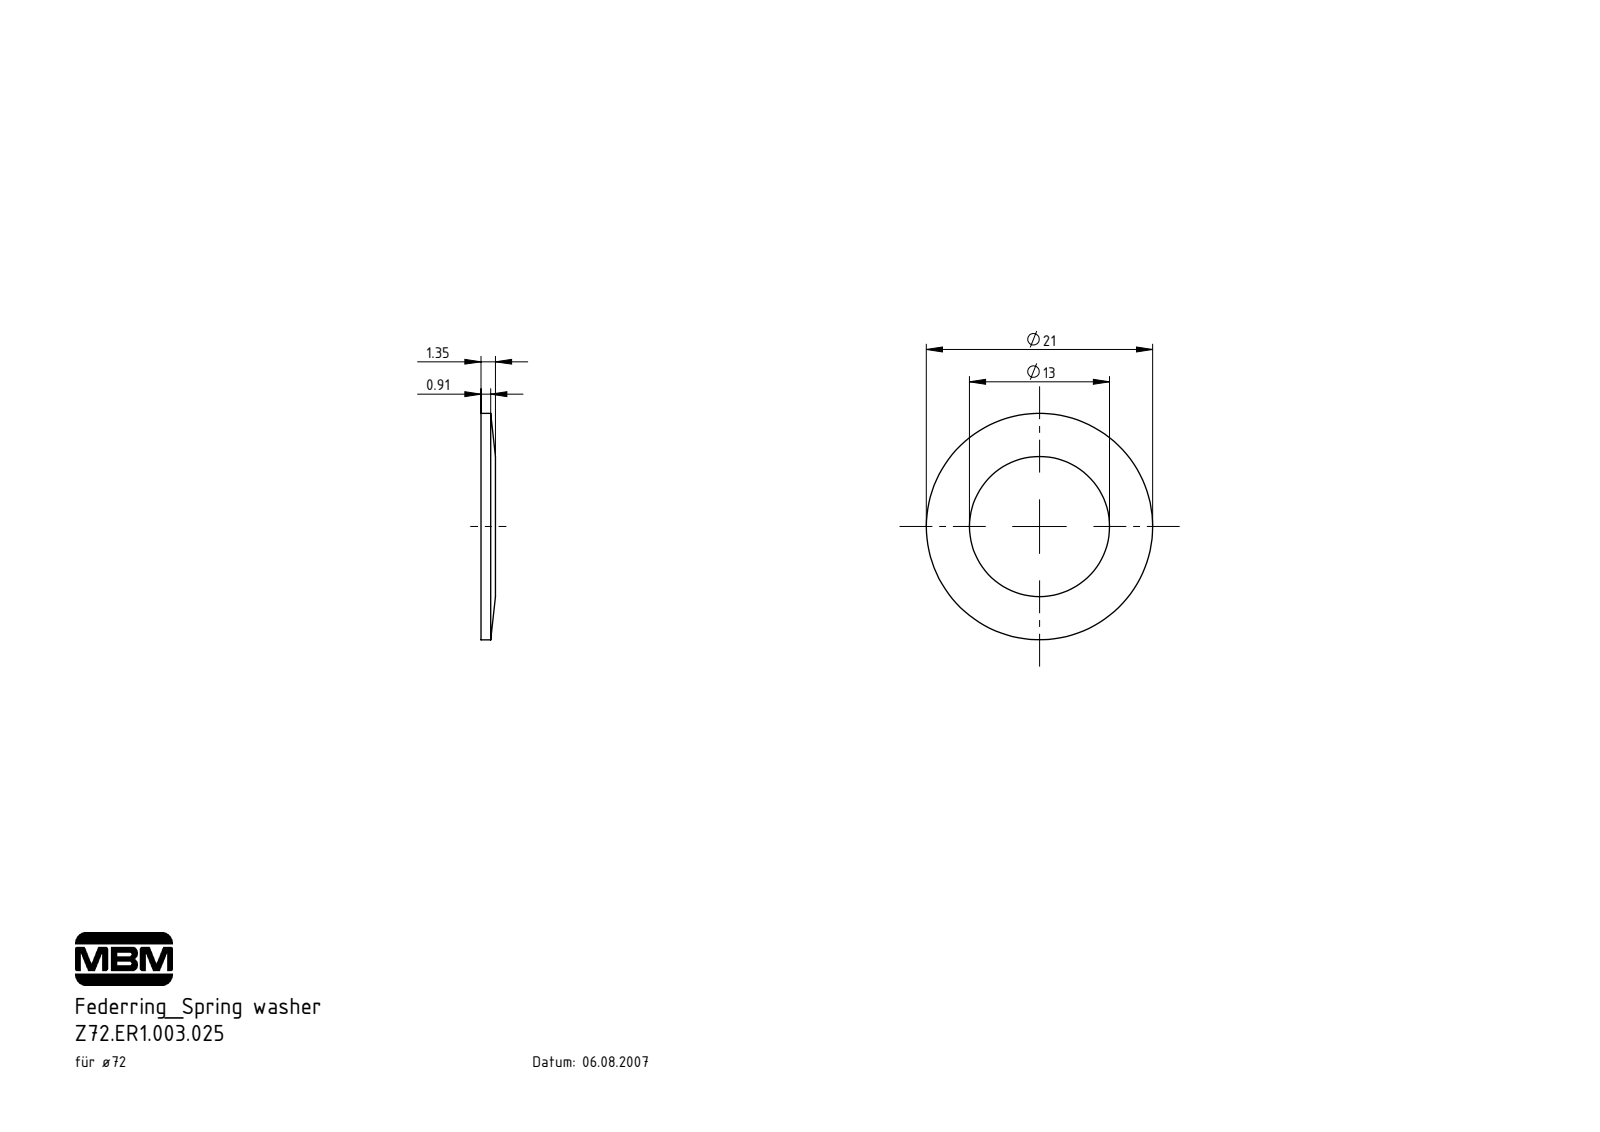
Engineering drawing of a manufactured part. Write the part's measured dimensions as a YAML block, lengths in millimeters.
part_name: "Z72.ER1.003.025"
step_written_by: "SolidWorks 2017 (AUTOMOTIVE_DESIGN)"
units: millimeters
bodies: {solids: 1, faces: 6, planar: 2, cylindrical: 4, other: 0}
overall_size: [21, 21, 0.9]
volume: 192
surface_area: 523
round_holes:
  - {diameter: 13, count: 1}
round_bosses_or_shafts:
  - {diameter: 21, count: 1}
face_to_face_distances: [0.9]
